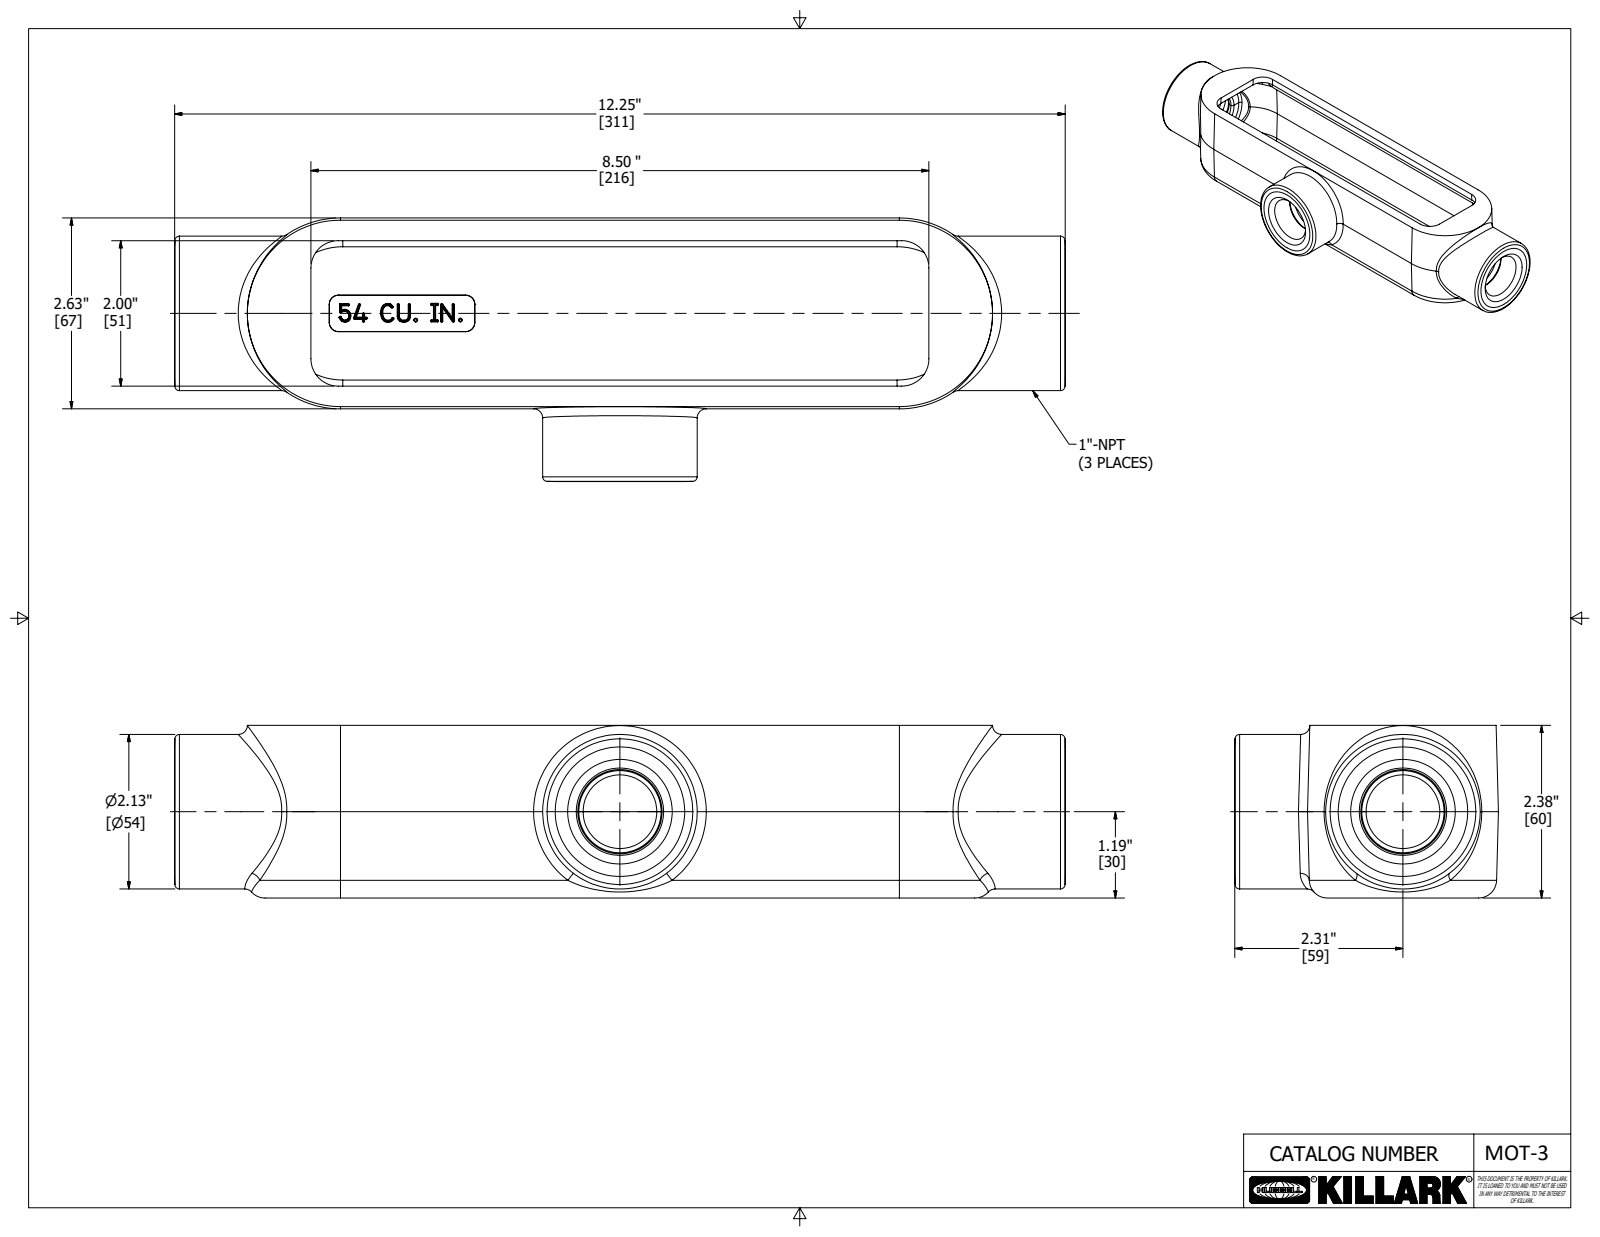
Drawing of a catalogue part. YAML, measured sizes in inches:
part_name: "21293"
step_written_by: "Autodesk Inventor 2020 (AUTOMOTIVE_DESIGN)"
units: inches
bodies: {solids: 1, faces: 530, planar: 255, cylindrical: 21, other: 254}
overall_size: [12.25, 3.625, 2.375]
volume: 22.05
surface_area: 187.2
round_holes:
  - {diameter: 1.013, count: 2}
  - {diameter: 1.321, count: 2}
round_bosses_or_shafts:
  - {diameter: 2.125, count: 2}
partial_cylinders:
  - {radius: 0.187, count: 6}
  - {radius: 0.25, count: 2}
  - {radius: 0.812, count: 1}
face_to_face_distances: [0.187, 2.437, 2.625, 2.25, 2.187, 2.375, 0.031, 2.343, 2.156, 0.094]
